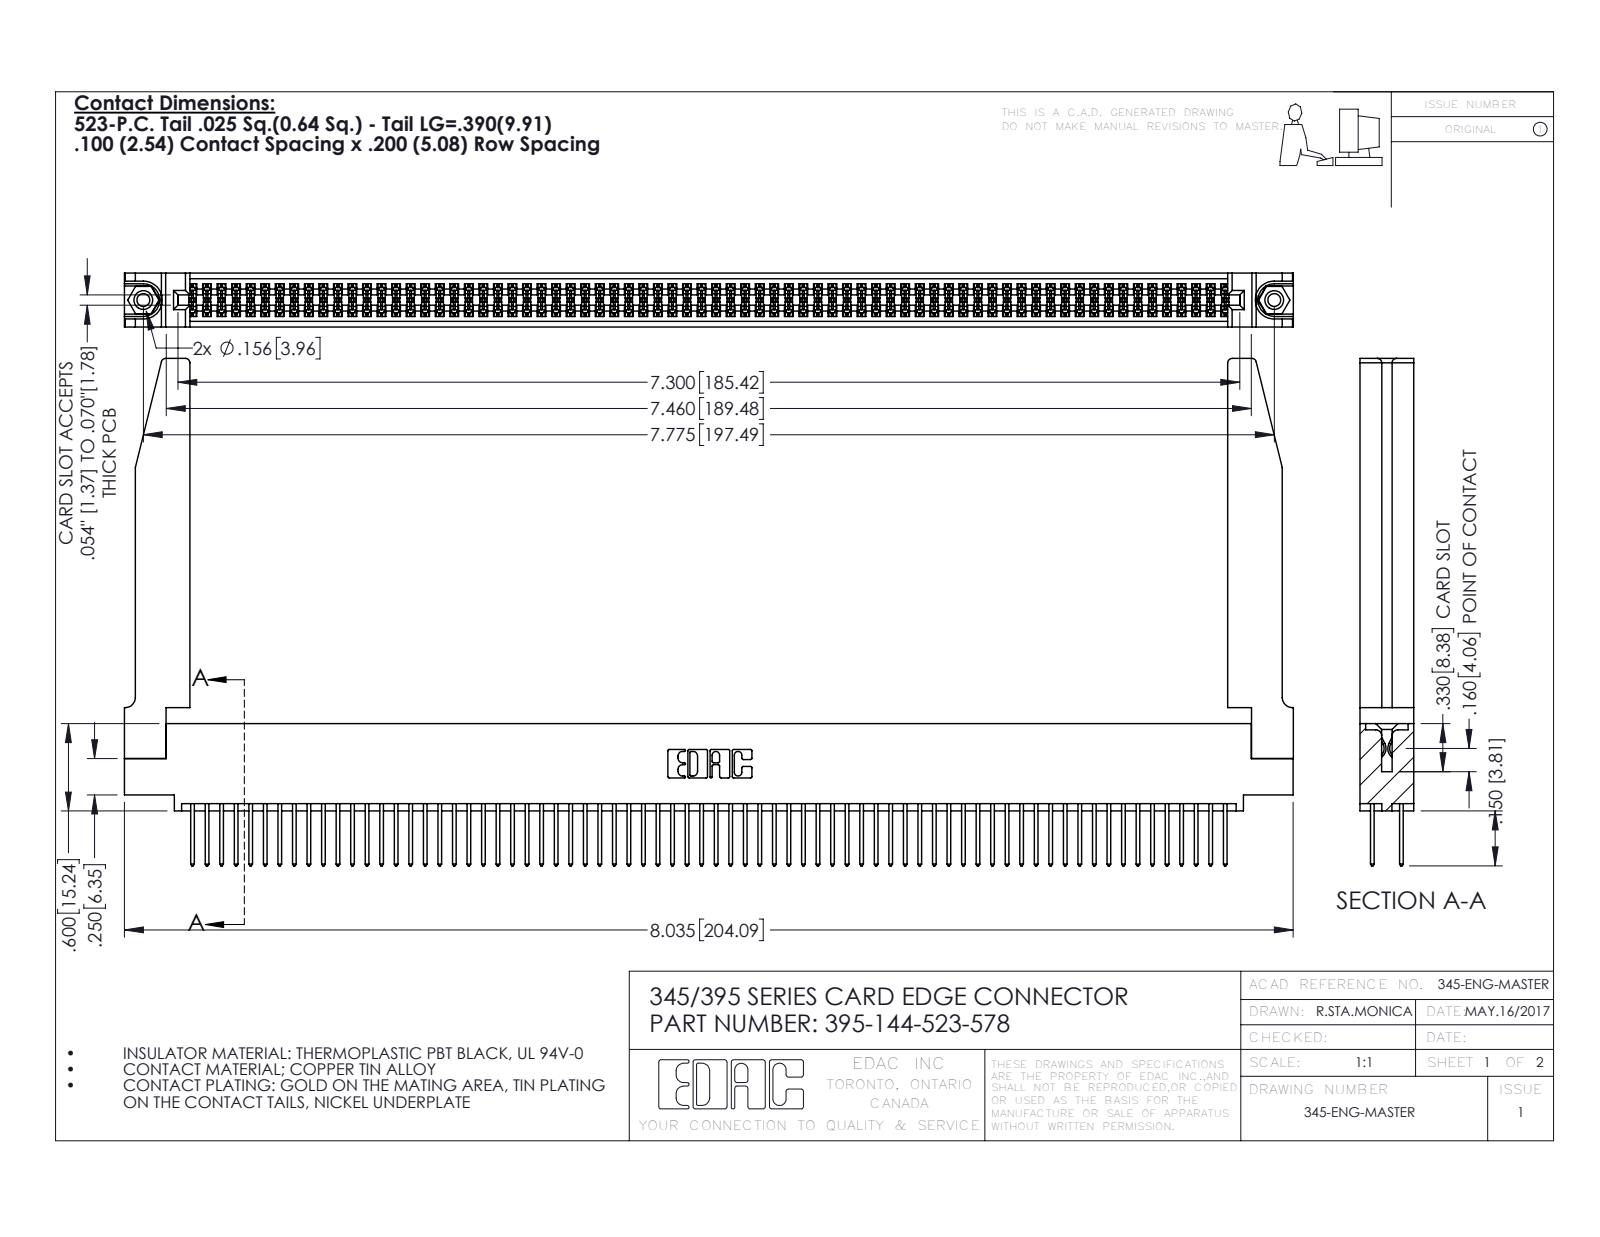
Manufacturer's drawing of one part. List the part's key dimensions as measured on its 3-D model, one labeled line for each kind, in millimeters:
Part name (STEP PRODUCT): 345-292-001_345-293-123; 345-250-001_345-250-001-102; 345 Part_0.110 Offset - 0.156 Dia-TH; 395-144-523-578 (+1 more)
STEP written by: SolidWorks 2016 (CONFIG_CONTROL_DESIGN)
Units: millimetres
Bodies: 149 solids, 7564 faces (4978 planar, 2534 cylindrical, 52 other)
Overall size (bounding box): 204.1 × 88.6 × 9.4
Volume: 28 100 mm³ · Surface area: 38 880 mm²
Round holes (diameter × count): ⌀2.3 ×2, ⌀3.2 ×2, ⌀4 ×2, ⌀1.6 ×1
Round bosses / shafts (diameter × count): ⌀3.9 ×2
Partial cylindrical surfaces — rounded edges, fillets, slot ends (radius × count): R0.2 ×216, R0.3 ×144, R0.3 ×22, R0.8 ×8, R0.2 ×6, R0.8 ×6, R0.7 ×3, R0.4 ×2
Main face-to-face distances: 1.8, 7.6, 9.4, 5.1, 2.5, 6.9, 0.6, 5.7, 4.4, 3.8
Hole centre spacings: 6.9, 191.5, 197.5
